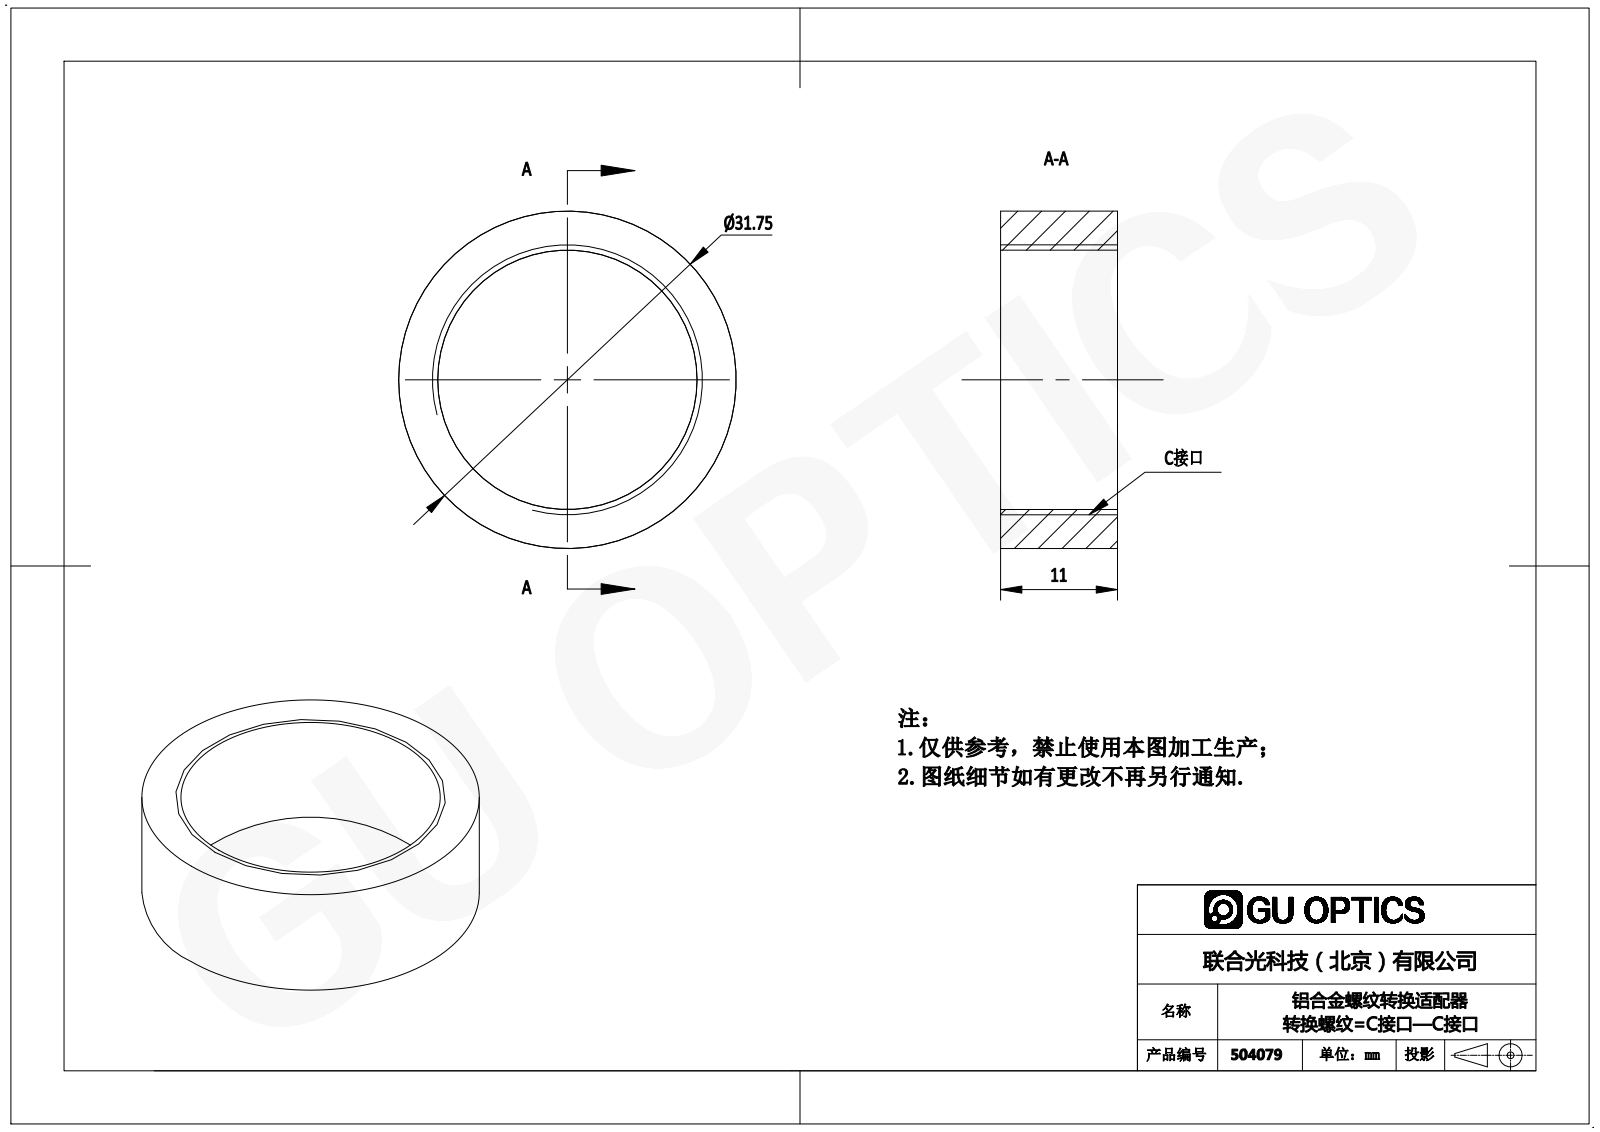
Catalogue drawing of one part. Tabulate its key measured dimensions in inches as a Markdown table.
| quantity | value |
| --- | --- |
| part name | 504079 |
| STEP written by | SolidWorks 2016 (AUTOMOTIVE_DESIGN) |
| units | inches |
| bodies | 1 solid, 6 faces (2 planar, 4 cylindrical, 0 other) |
| overall size | 1.25 × 1.25 × 0.433 |
| volume | 0.218 in³ |
| surface area | 4.013 in² |
| round holes (diameter × count) | 0.961 × 1 |
| round bosses / shafts (diameter × count) | 1.25 × 1 |
| main face-to-face distances | 0.433 |
